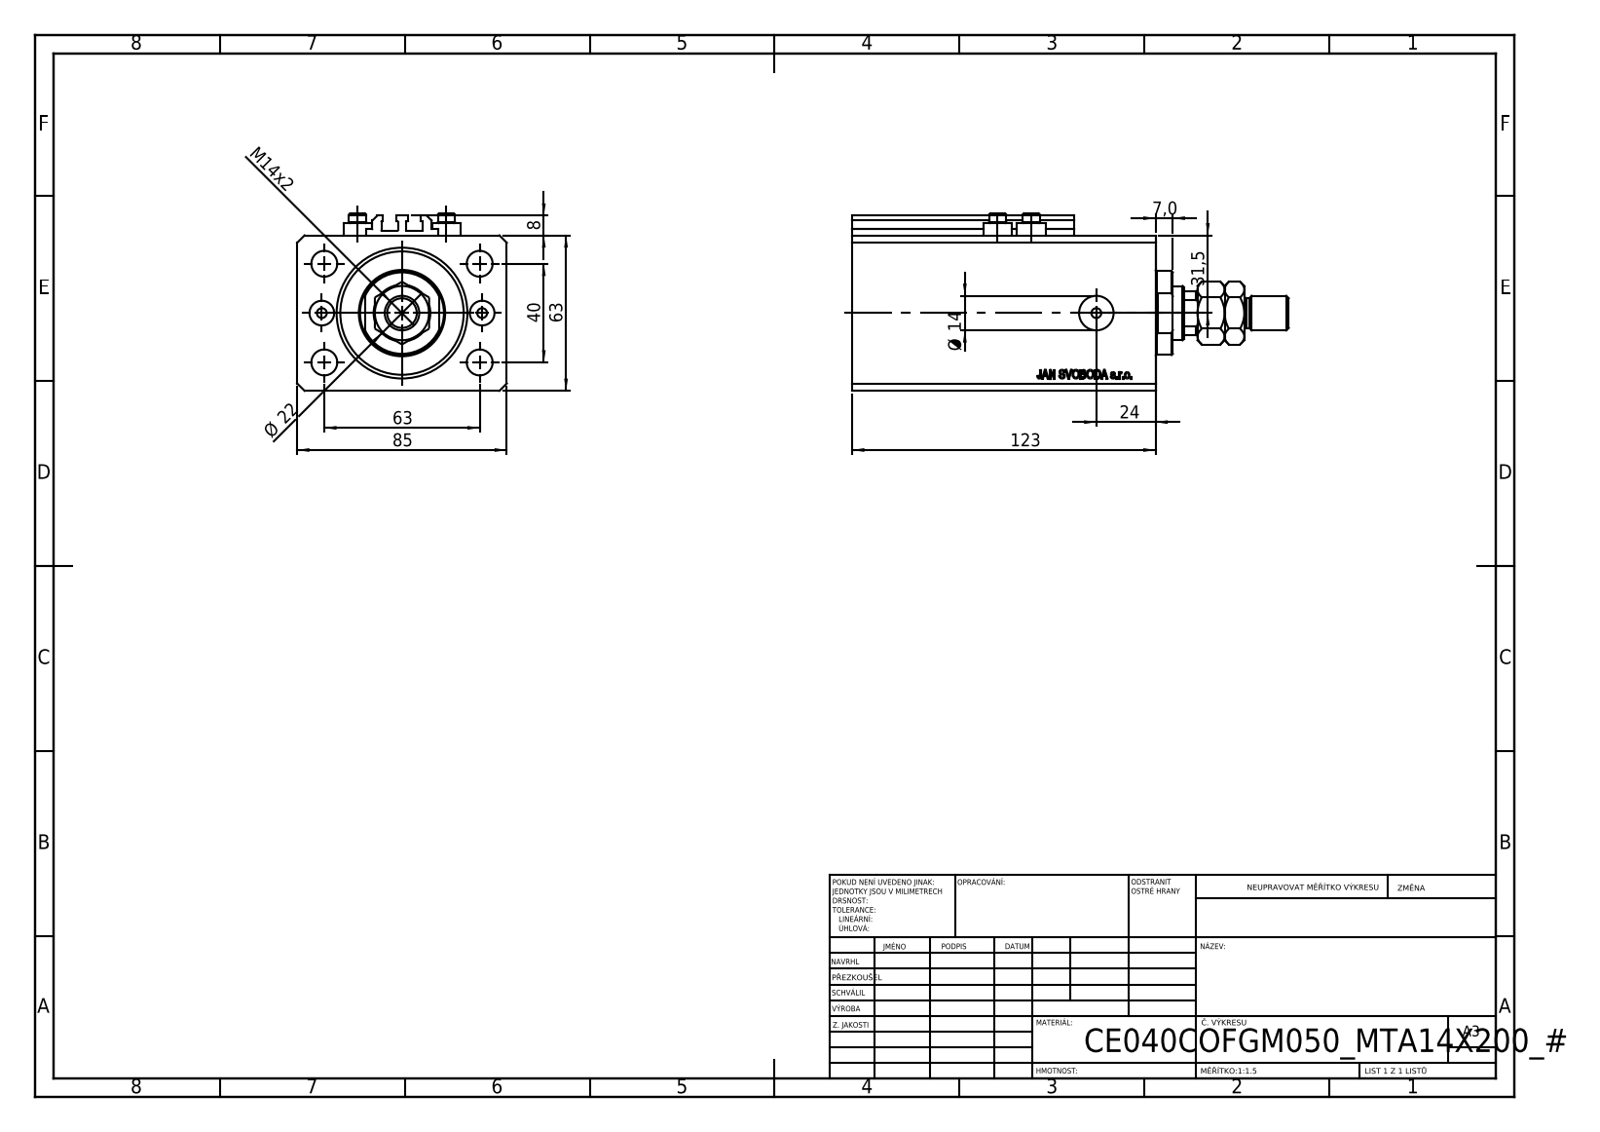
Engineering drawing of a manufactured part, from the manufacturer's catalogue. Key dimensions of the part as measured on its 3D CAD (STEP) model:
Part name (STEP PRODUCT): V250CE_VC_C; V250CE_C_VCP; MTA; V250CE_C_Body (+1 more)
STEP written by: SolidWorks 2019 (CONFIG_CONTROL_DESIGN)
Units: millimetres
Bodies: 8 solids, 1082 faces (518 planar, 90 cylindrical, 474 other)
Overall size (bounding box): 177 × 85 × 72
Volume: 141 393 mm³ · Surface area: 116 728 mm²
Round holes (diameter × count): ⌀4 ×8, ⌀10.5 ×4, ⌀10 ×2, ⌀14 ×2, ⌀12.5 ×1, ⌀22 ×1, ⌀40 ×1, ⌀53 ×1
Round bosses / shafts (diameter × count): ⌀11.6 ×4, ⌀7 ×4, ⌀34 ×1, ⌀14 ×1, ⌀12 ×1
Partial cylindrical surfaces — rounded edges, fillets, slot ends (radius × count): R0.2 ×10, R10.5 ×1
Main face-to-face distances: 63, 85, 123, 17, 106, 11.4, 94.6, 111.6, 10, 2.5
Hole centre spacings: 20.02, 37.31, 67.05, 13.6, 32.5, 36, 38.48, 40
